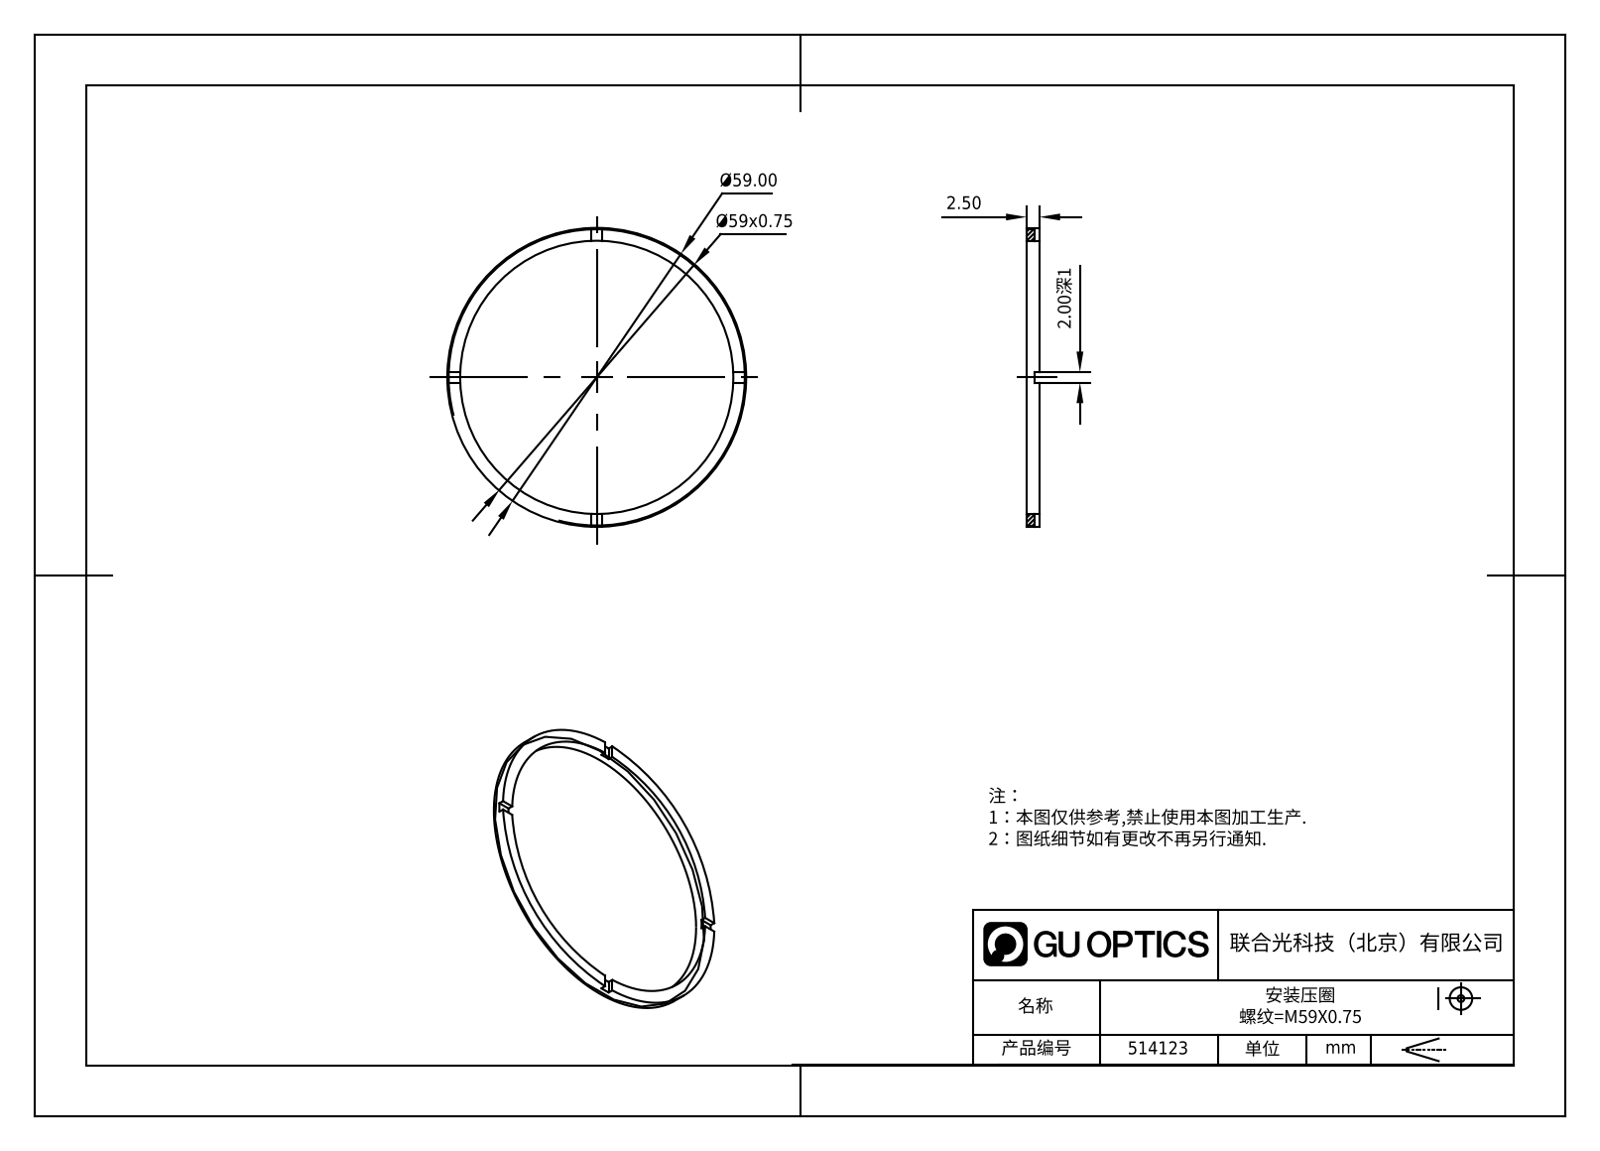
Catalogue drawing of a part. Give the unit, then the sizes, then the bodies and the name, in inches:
Units: inches
Overall size (bounding box): 2.323 × 2.323 × 0.098
Round holes (diameter × count): ⌀2.126 ×1
Round bosses / shafts (diameter × count): ⌀2.323 ×1
Main face-to-face distances: 0.098, 0.059, 0.039, 0.079
Volume: 0.066 in³ · Surface area: 2.757 in²
Bodies: 1 solid, 21 faces (17 planar, 4 cylindrical, 0 other)
Part name (STEP PRODUCT): 514123
STEP written by: SolidWorks 2020 (CONFIG_CONTROL_DESIGN)
